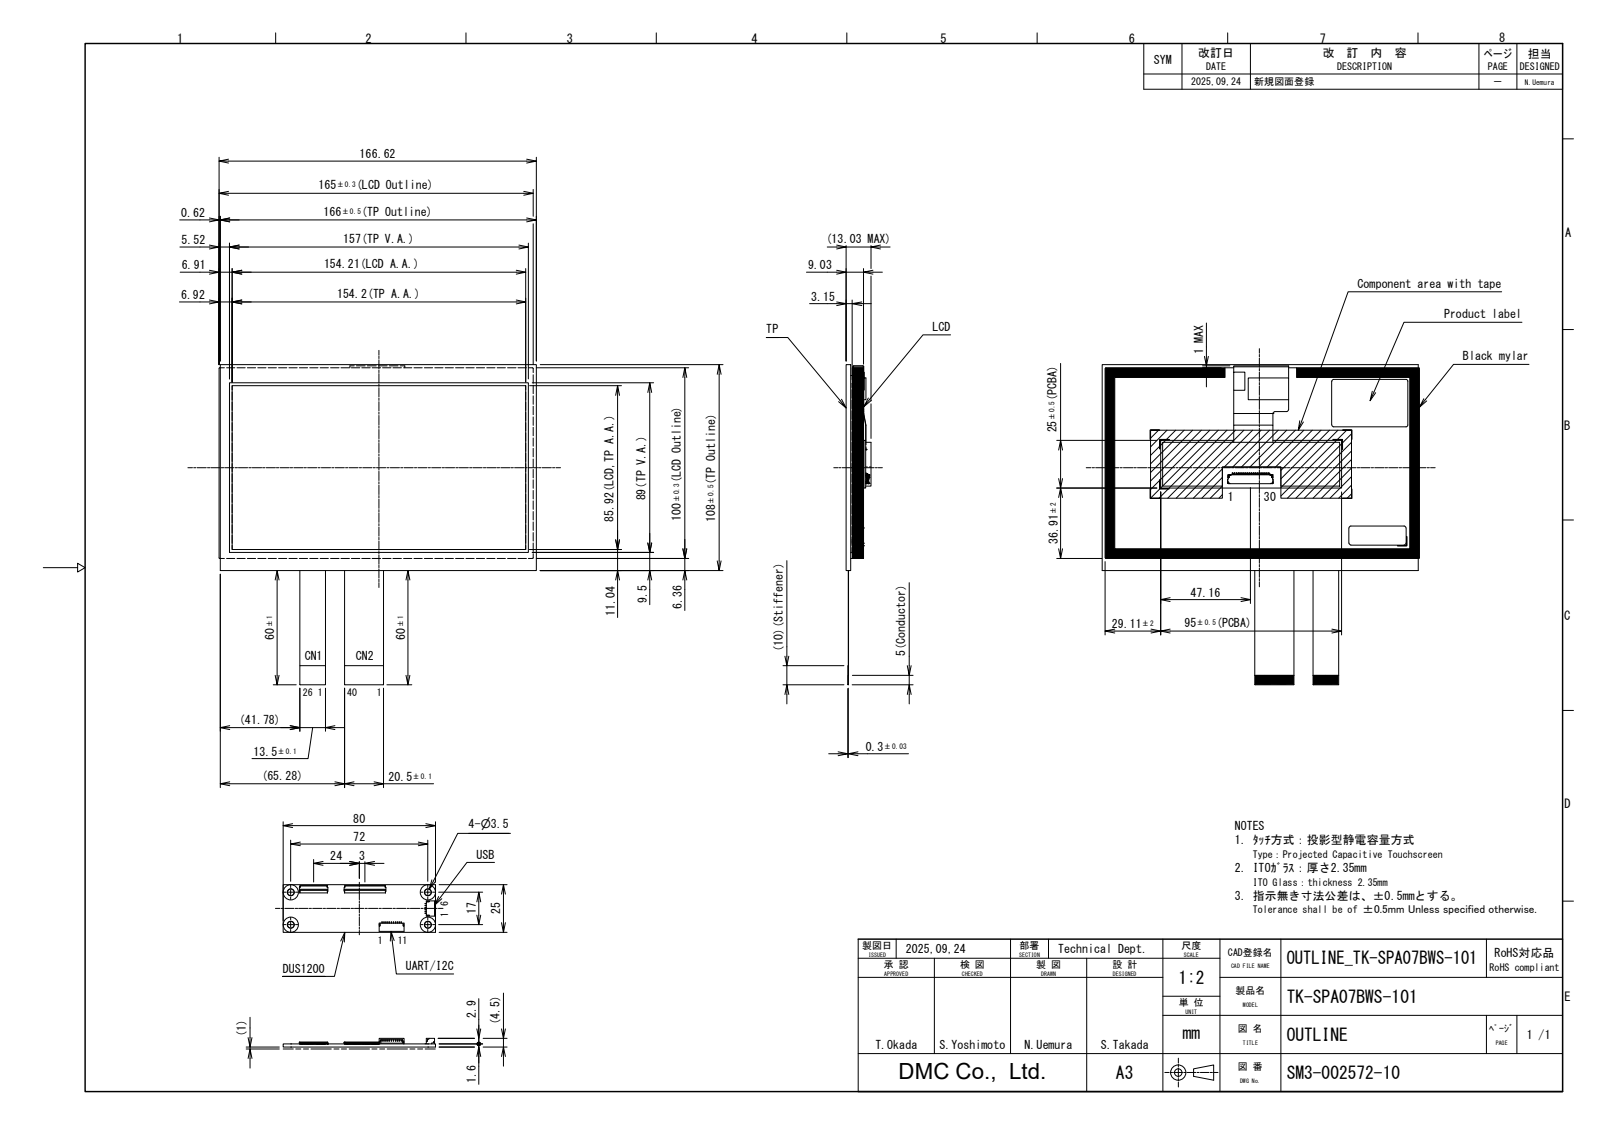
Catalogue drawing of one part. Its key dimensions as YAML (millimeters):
part_name: "TK-SPA07BWS-101"
step_written_by: "Autodesk Inventor 2024 (AUTOMOTIVE_DESIGN)"
units: millimeters
bodies: {solids: 1, faces: 1374, planar: 1162, cylindrical: 212, other: 0}
overall_size: [168, 166.62, 13.03]
volume: 148439
surface_area: 79565
partial_cylinders:
  - {radius: 0.1, count: 95}
  - {radius: 1, count: 10}
  - {radius: 0.2, count: 6}
  - {radius: 0.33, count: 4}
  - {radius: 0.15, count: 2}
  - {radius: 0.3, count: 2}
  - {radius: 0.42, count: 2}
face_to_face_distances: [2.35, 0.8, 3.15, 8.98, 5.83, 6.63, 7.88, 9.03, 5.88, 6.68]
